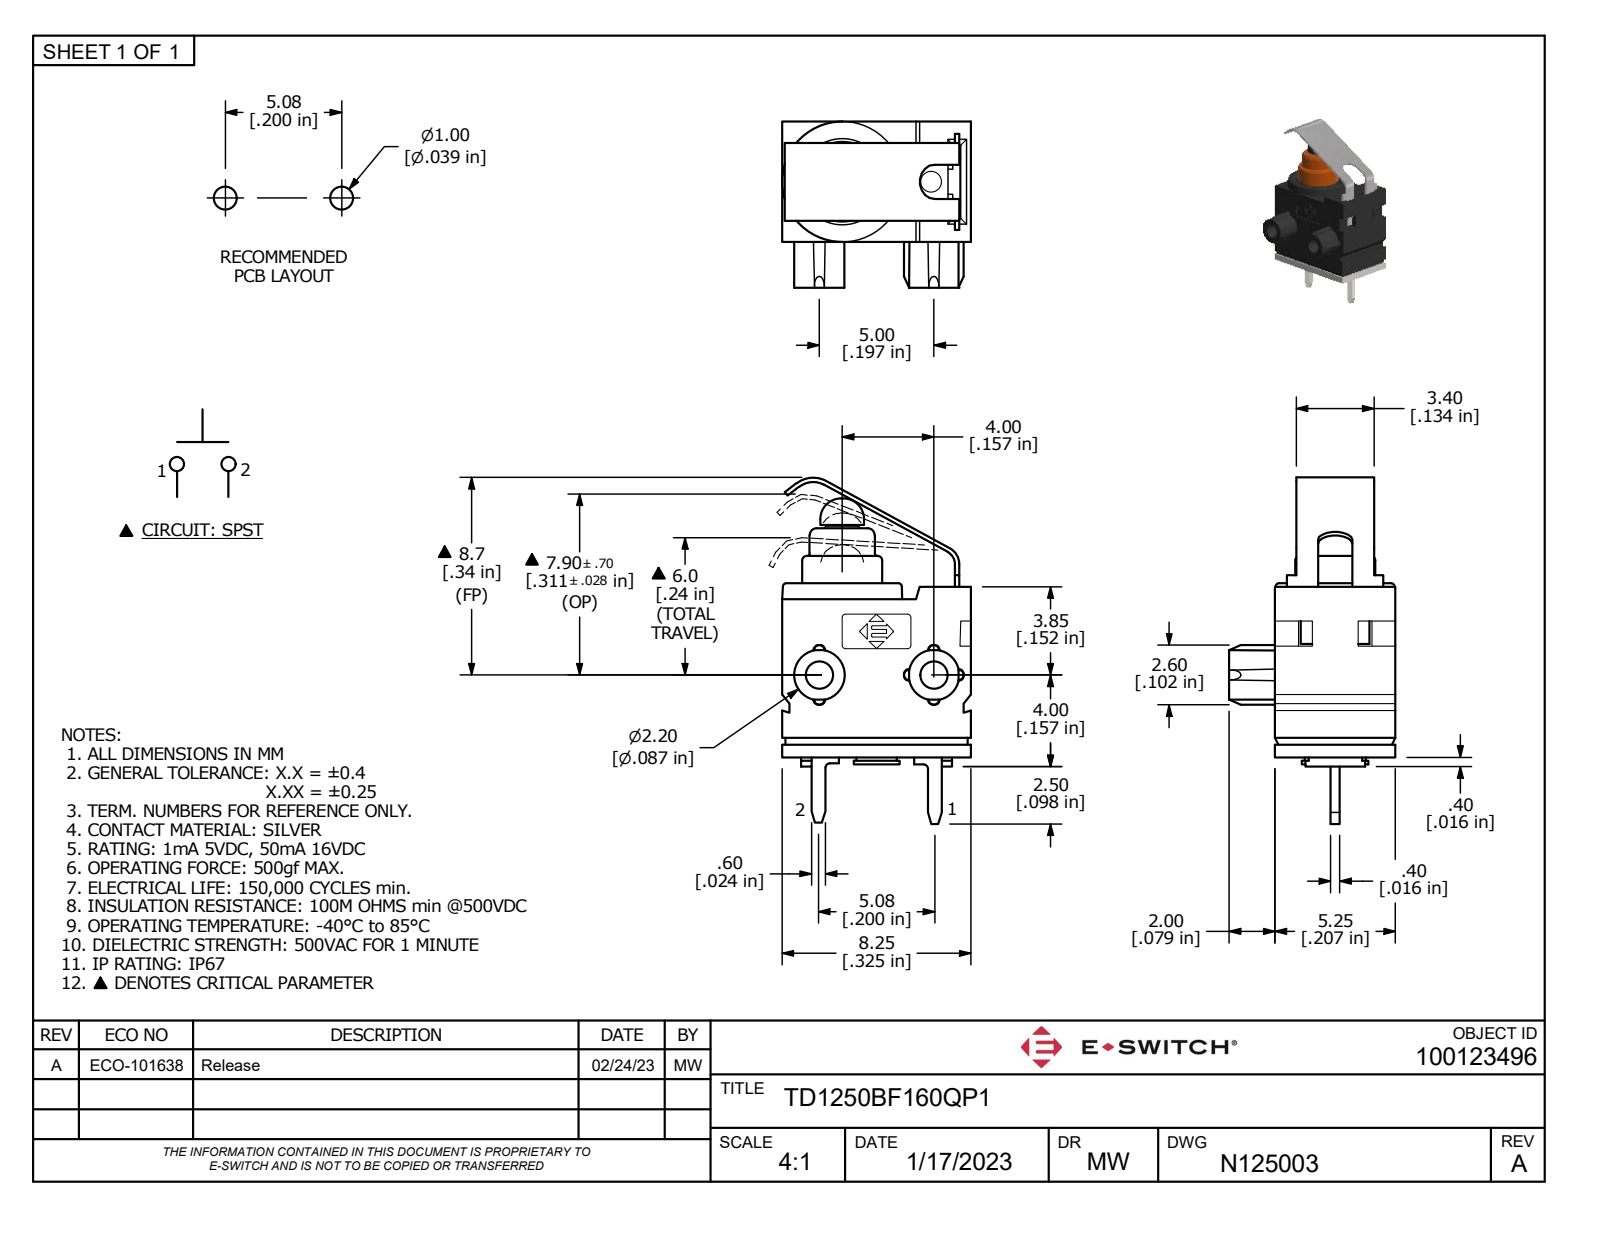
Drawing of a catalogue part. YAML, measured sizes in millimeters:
part_name: "TD1250BF160QP1"
step_written_by: "Autodesk Inventor 2022 (AUTOMOTIVE_DESIGN)"
units: millimeters
bodies: {solids: 1, faces: 255, planar: 196, cylindrical: 47, other: 12}
overall_size: [15.12, 8.25, 7.25]
volume: 354
surface_area: 513
round_holes:
  - {diameter: 1.2, count: 2}
  - {diameter: 4.65, count: 1}
round_bosses_or_shafts:
  - {diameter: 4.5, count: 1}
  - {diameter: 3.5, count: 1}
  - {diameter: 2.85, count: 1}
  - {diameter: 2.2, count: 1}
  - {diameter: 1.9, count: 1}
  - {diameter: 1.2, count: 1}
partial_cylinders:
  - {radius: 0.2, count: 14}
  - {radius: 0.15, count: 4}
  - {radius: 0.6, count: 1}
  - {radius: 0.75, count: 1}
  - {radius: 0.79, count: 1}
  - {radius: 1, count: 1}
  - {radius: 1.1, count: 1}
  - {radius: 1.19, count: 1}
face_to_face_distances: [5.24, 8.24, 0.55, 6.9, 7.45, 0.5, 7.24, 7.75, 0.95, 0.69]
hole_center_spacings: [5]
